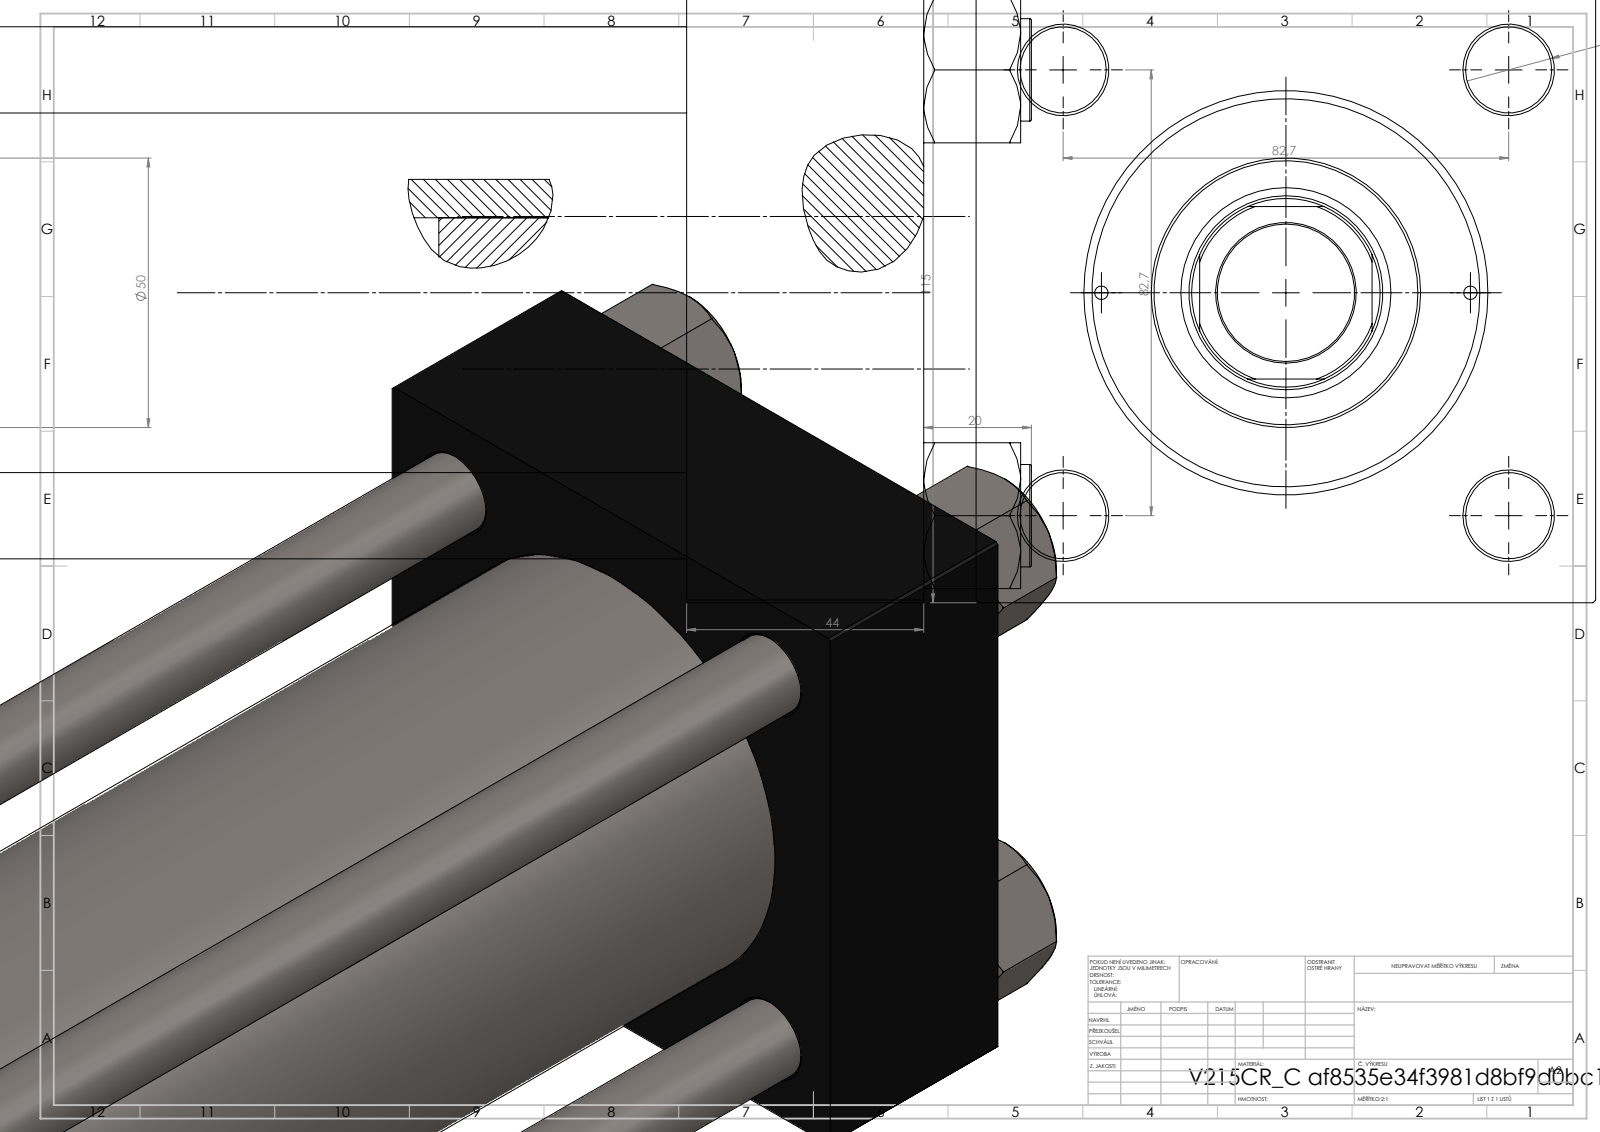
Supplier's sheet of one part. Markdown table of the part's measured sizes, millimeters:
| quantity | value |
| --- | --- |
| part name | V215CR_C_Body; V215CR_C_TYCINKA; FEMALE_PART_FOR_DFA; V215CR_VCP_C (+2 more) |
| STEP written by | SolidWorks 2019 (CONFIG_CONTROL_DESIGN) |
| units | millimeters |
| bodies | 12 solids, 1235 faces (588 planar, 99 cylindrical, 548 other) |
| overall size | 460 × 115 × 115 |
| volume | 2 435 000 mm³ |
| surface area | 473 037 mm² |
| round holes (diameter × count) | 16 × 4, 2.5 × 2, 7 × 2, 26.44 × 2, 35 × 2, 25.5 × 1, 39 × 1, 61 × 1, 72 × 1, 80 × 1 |
| round bosses / shafts (diameter × count) | 19 × 4, 86 × 1, 50 × 1, 44 × 1, 36 × 1, 27 × 1, 25 × 1 |
| partial cylindrical surfaces (radius × count) | 9.5 × 1, 15 × 1, 17.5 × 1 |
| main face-to-face distances | 115, 44, 409, 365, 340, 296, 69, 90, 250, 380.3 |
| hole center spacings | 41.96, 58.48, 82.7, 86.17, 34.25, 116.96, 68.5, 341 |
